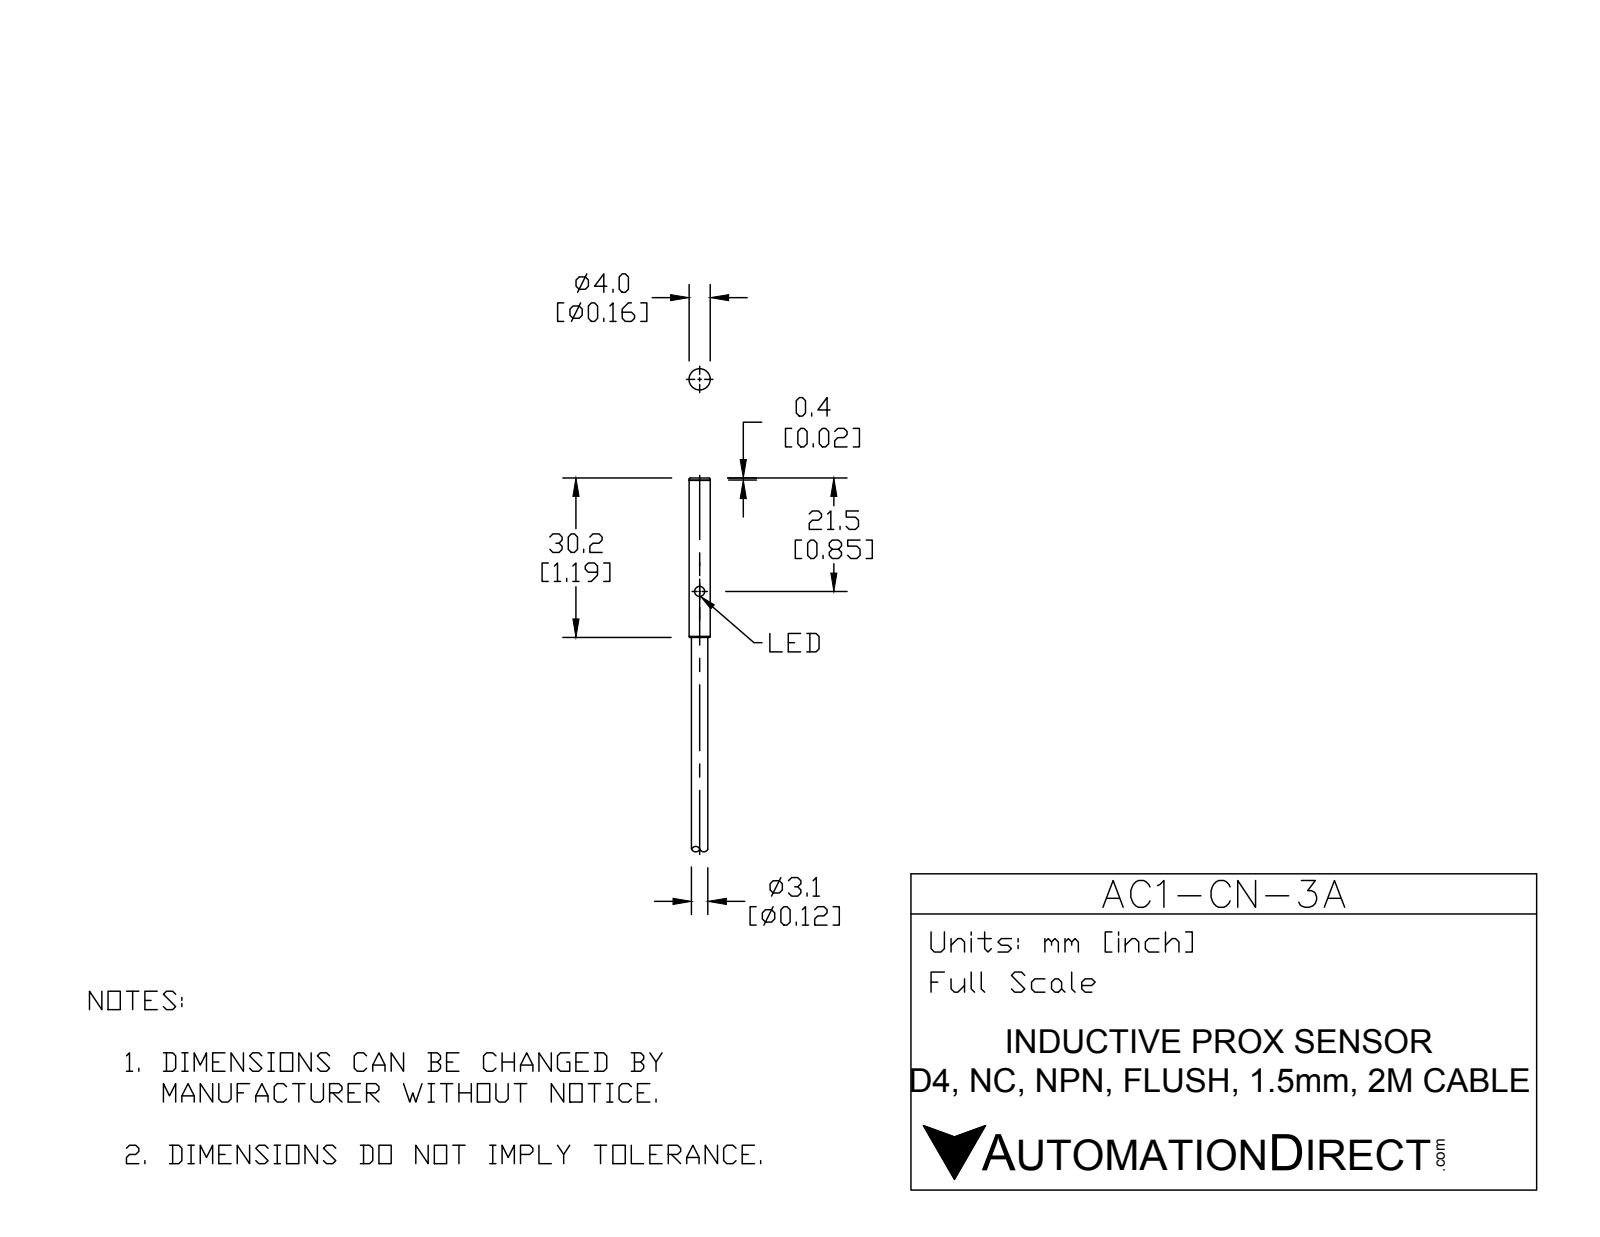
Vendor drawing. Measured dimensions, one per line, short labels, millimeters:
name: AC1-CN-3A
written by: SolidWorks 2015 (CONFIG_CONTROL_DESIGN)
unit: mm
bodies: 2 solids, 20 faces (6 planar, 8 cylindrical, 6 other)
size: 80.2 × 4 × 4
volume: 756 mm³; area: 905 mm²
holes: 1× ⌀1.9
bosses: 1× ⌀4, 1× ⌀3.1
face distances: 30.2, 50, 80.2, 79.8, 29.8, 0.4
